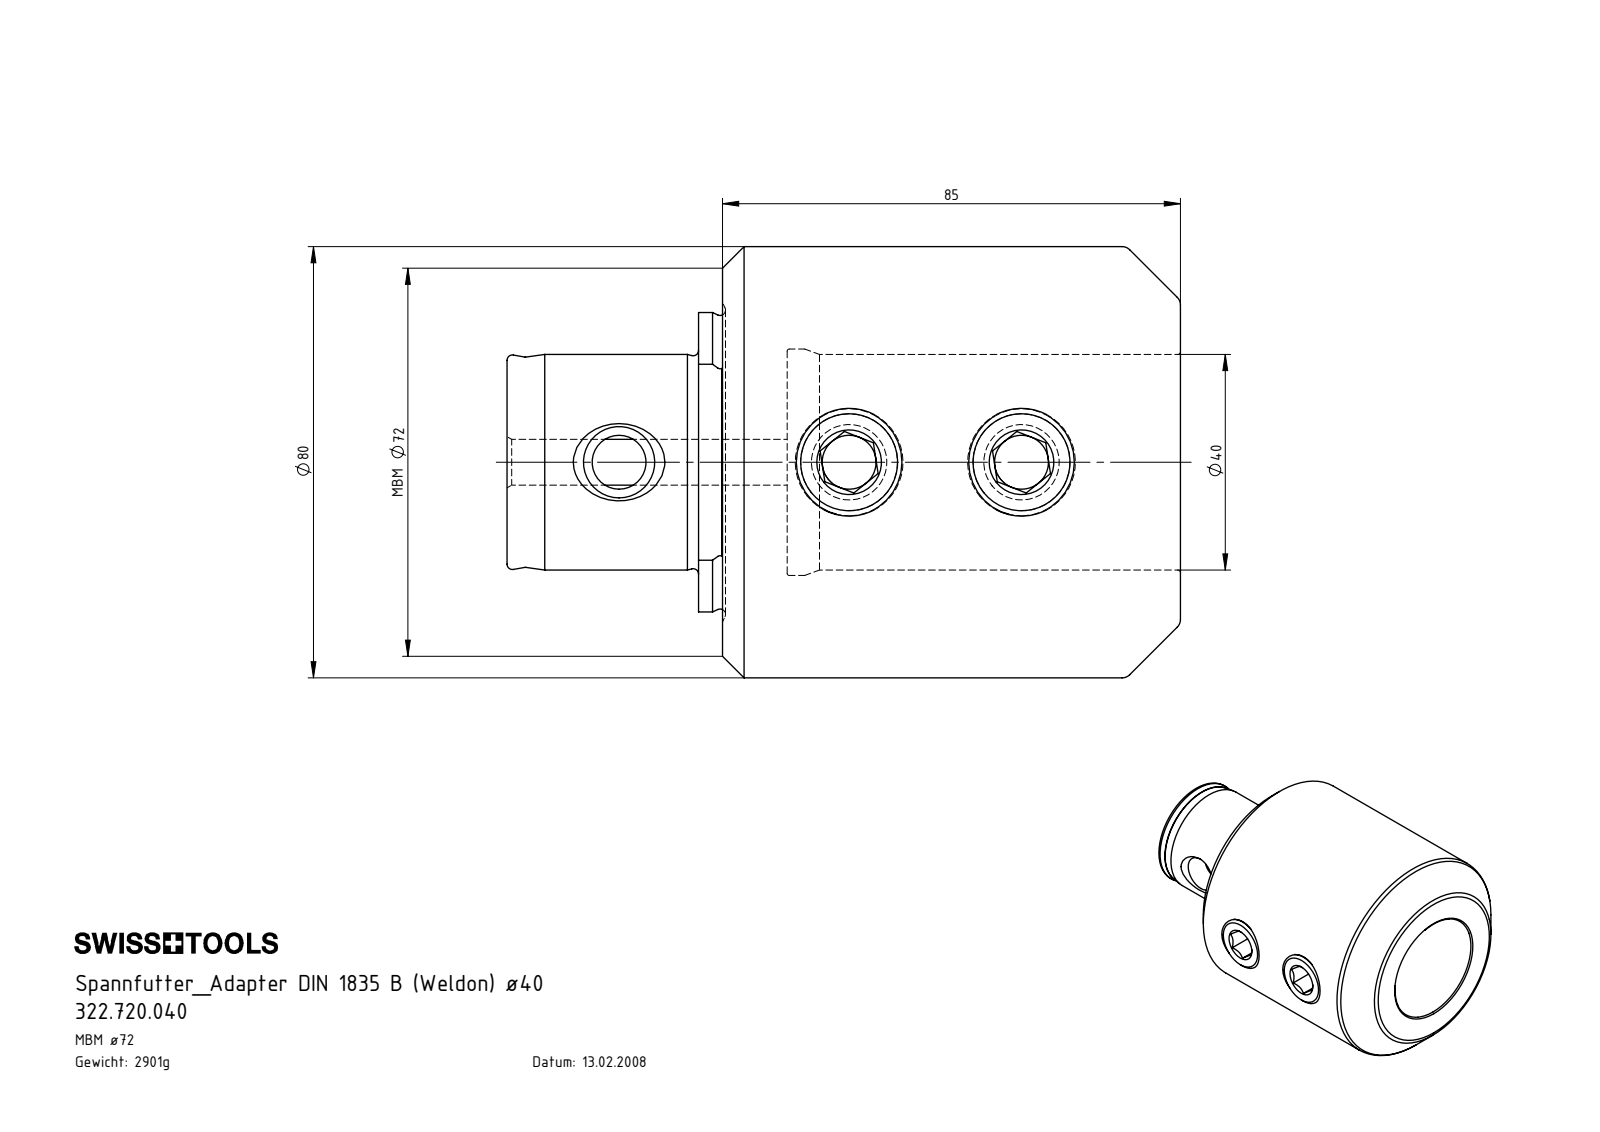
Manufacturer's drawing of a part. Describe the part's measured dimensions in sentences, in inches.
The part is named "MB7-W40.K01.085_C; W40-ER1.001.020; MB7.W40.K01.085". Its 3-D file was written by "SolidWorks 2017 (AUTOMOTIVE_DESIGN)". It is 3 solids with 86 faces: 39 planar, 14 cylindrical and 33 other. Overall it measures 4.921 by 3.15 by 3.15 inches. Its volume is 22.39 cubic inches and its surface area 78.54 square inches. Round holes: 3 of diameter 0.394, 2 of diameter 0.709, 1 of diameter 0.335, 1 of diameter 1.575, 1 of diameter 1.654. Round bosses or shafts: 2 of diameter 0.787, 1 of diameter 3.15. Partial cylindrical surfaces (rounded edges, fillets, slot ends): 1 of radius 1.093. The main face-to-face distances are 3.346, 0.472, 2.874, 1.575, 2.047, 4.921, 1.4, 0.175, 0.648, 3.522. The hole center spacings are 1.26, 1.681, 2.941.
